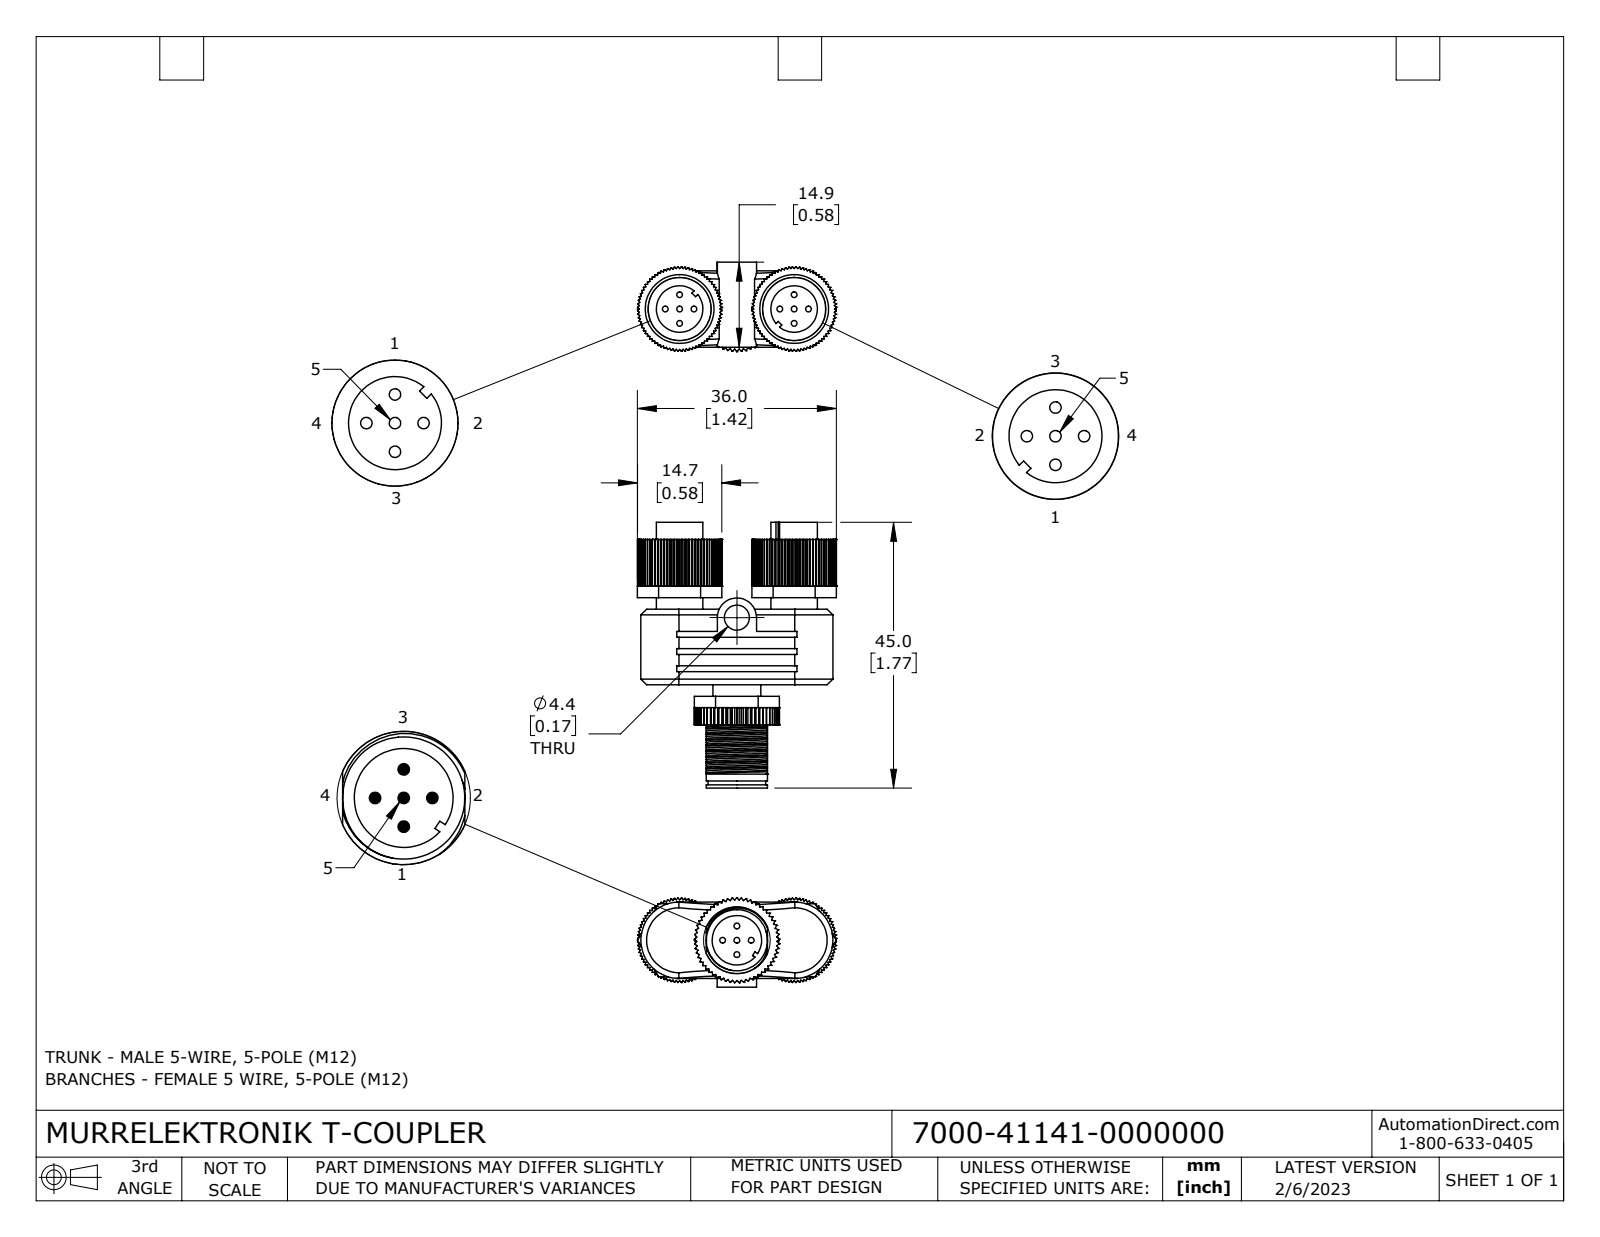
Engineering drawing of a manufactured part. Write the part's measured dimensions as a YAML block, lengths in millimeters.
part_name: "7000-41141-0000000"
step_written_by: "SolidWorks 2021 (CONFIG_CONTROL_DESIGN)"
units: millimeters
bodies: {solids: 1, faces: 995, planar: 602, cylindrical: 308, other: 85}
overall_size: [46.39, 34.73, 15.62]
volume: 9860
surface_area: 6505
round_holes:
  - {diameter: 1, count: 10}
  - {diameter: 11, count: 2}
  - {diameter: 4.37, count: 1}
  - {diameter: 8.63, count: 1}
round_bosses_or_shafts:
  - {diameter: 1, count: 5}
  - {diameter: 8.12, count: 2}
  - {diameter: 10.66, count: 1}
  - {diameter: 10.05, count: 1}
  - {diameter: 8.38, count: 1}
partial_cylinders:
  - {radius: 6.67, count: 2}
  - {radius: 7.37, count: 2}
  - {radius: 3.42, count: 1}
  - {radius: 5.82, count: 1}
  - {radius: 7.43, count: 1}
  - {radius: 105.6, count: 1}
  - {radius: 105.61, count: 1}
face_to_face_distances: [9.98, 2, 15.2, 10, 9.99, 5, 27.35, 3, 9.96, 13.2]
hole_center_spacings: [2.5, 3.54, 20, 5, 10.31, 17.68, 20.16, 22.64]
